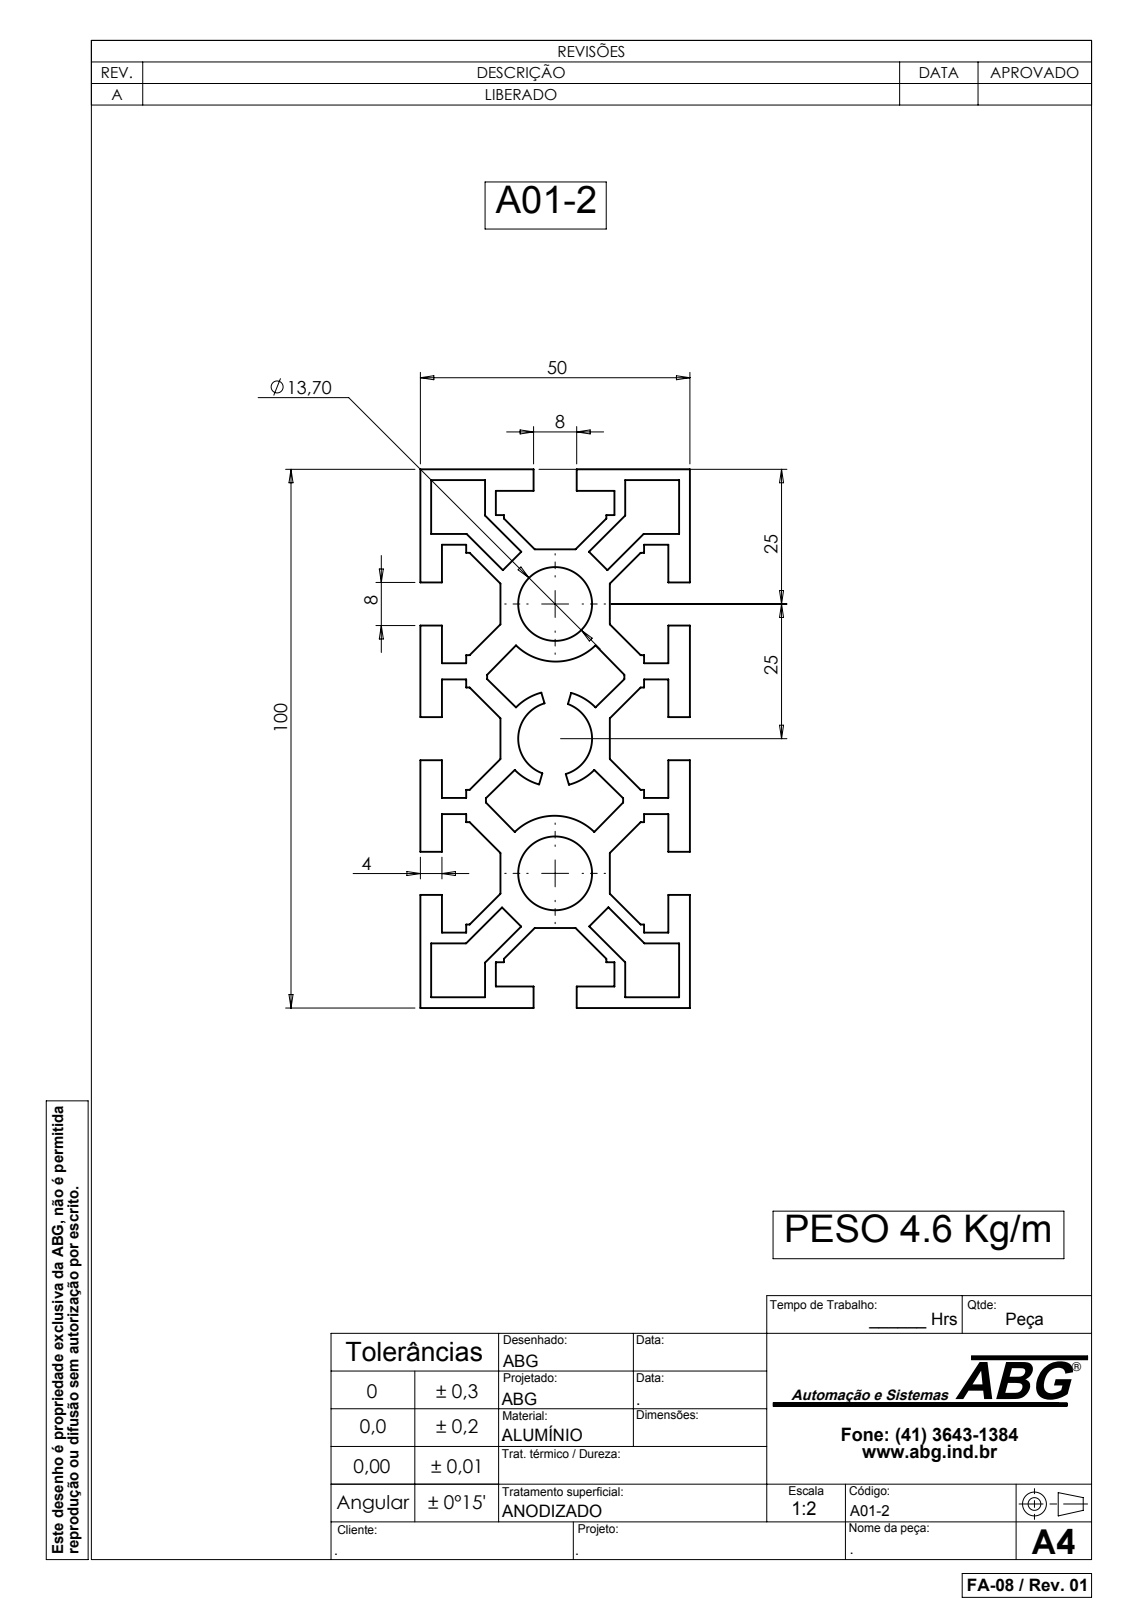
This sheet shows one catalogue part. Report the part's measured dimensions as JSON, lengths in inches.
{"part_name": "A01-2", "step_written_by": "SolidWorks 2007 (CONFIG_CONTROL_DESIGN)", "units": "inches", "bodies": {"solids": 1, "faces": 175, "planar": 162, "cylindrical": 13, "other": 0}, "overall_size": [236.22, 3.937, 1.969], "volume_in3": 686.5, "surface_area_in2": 11010, "round_holes": [[0.539, 3]], "partial_cylinders_radius": [[0.406, 2], [0.415, 2]], "face_to_face_distances": [0.079, 1.969, 0.394, 1.811, 0.157, 0.984, 0.472, 0.315, 1.654, 0.669], "hole_center_spacings": [0.984, 1.969]}
